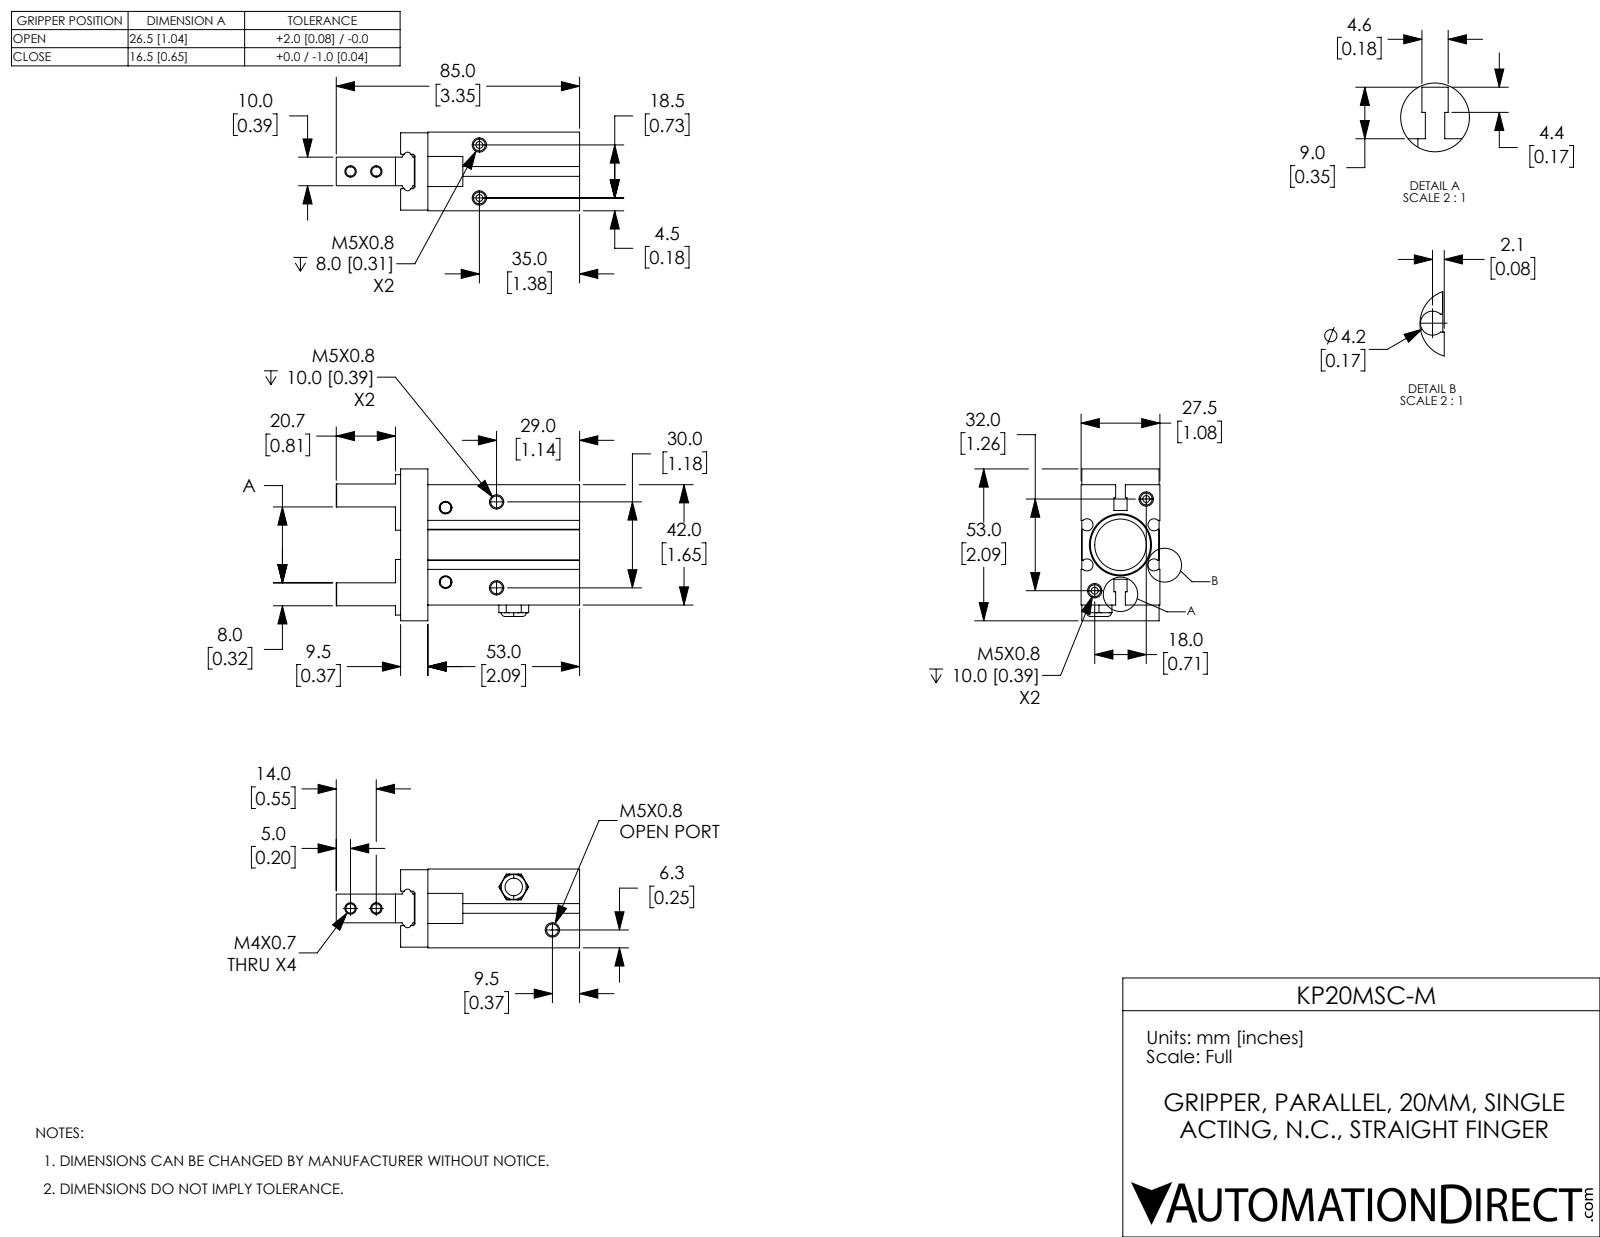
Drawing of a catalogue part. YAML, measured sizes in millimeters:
part_name: "KP20MSC-M-2; KP20MSC-M-1; KP20MSC-M; KP20MSC-M-3"
step_written_by: "SolidWorks 2017 (CONFIG_CONTROL_DESIGN)"
units: millimeters
bodies: {solids: 3, faces: 265, planar: 129, cylindrical: 66, other: 70}
overall_size: [85, 53, 27.5]
volume: 63777
surface_area: 22054
round_holes:
  - {diameter: 4.13, count: 8}
  - {diameter: 0.5, count: 2}
  - {diameter: 3.24, count: 2}
  - {diameter: 5.02, count: 2}
  - {diameter: 6.1, count: 1}
  - {diameter: 18, count: 1}
  - {diameter: 21, count: 1}
partial_cylinders:
  - {radius: 0.2, count: 8}
  - {radius: 1.25, count: 4}
  - {radius: 2.1, count: 4}
  - {radius: 0.5, count: 2}
face_to_face_distances: [8.5, 18.75, 27.5, 42, 27.2, 19, 8.2, 18.7, 8.25, 27.25]
hole_center_spacings: [18.36, 37.17, 45.94, 9, 12.13, 18.5, 20.18, 20.6]
